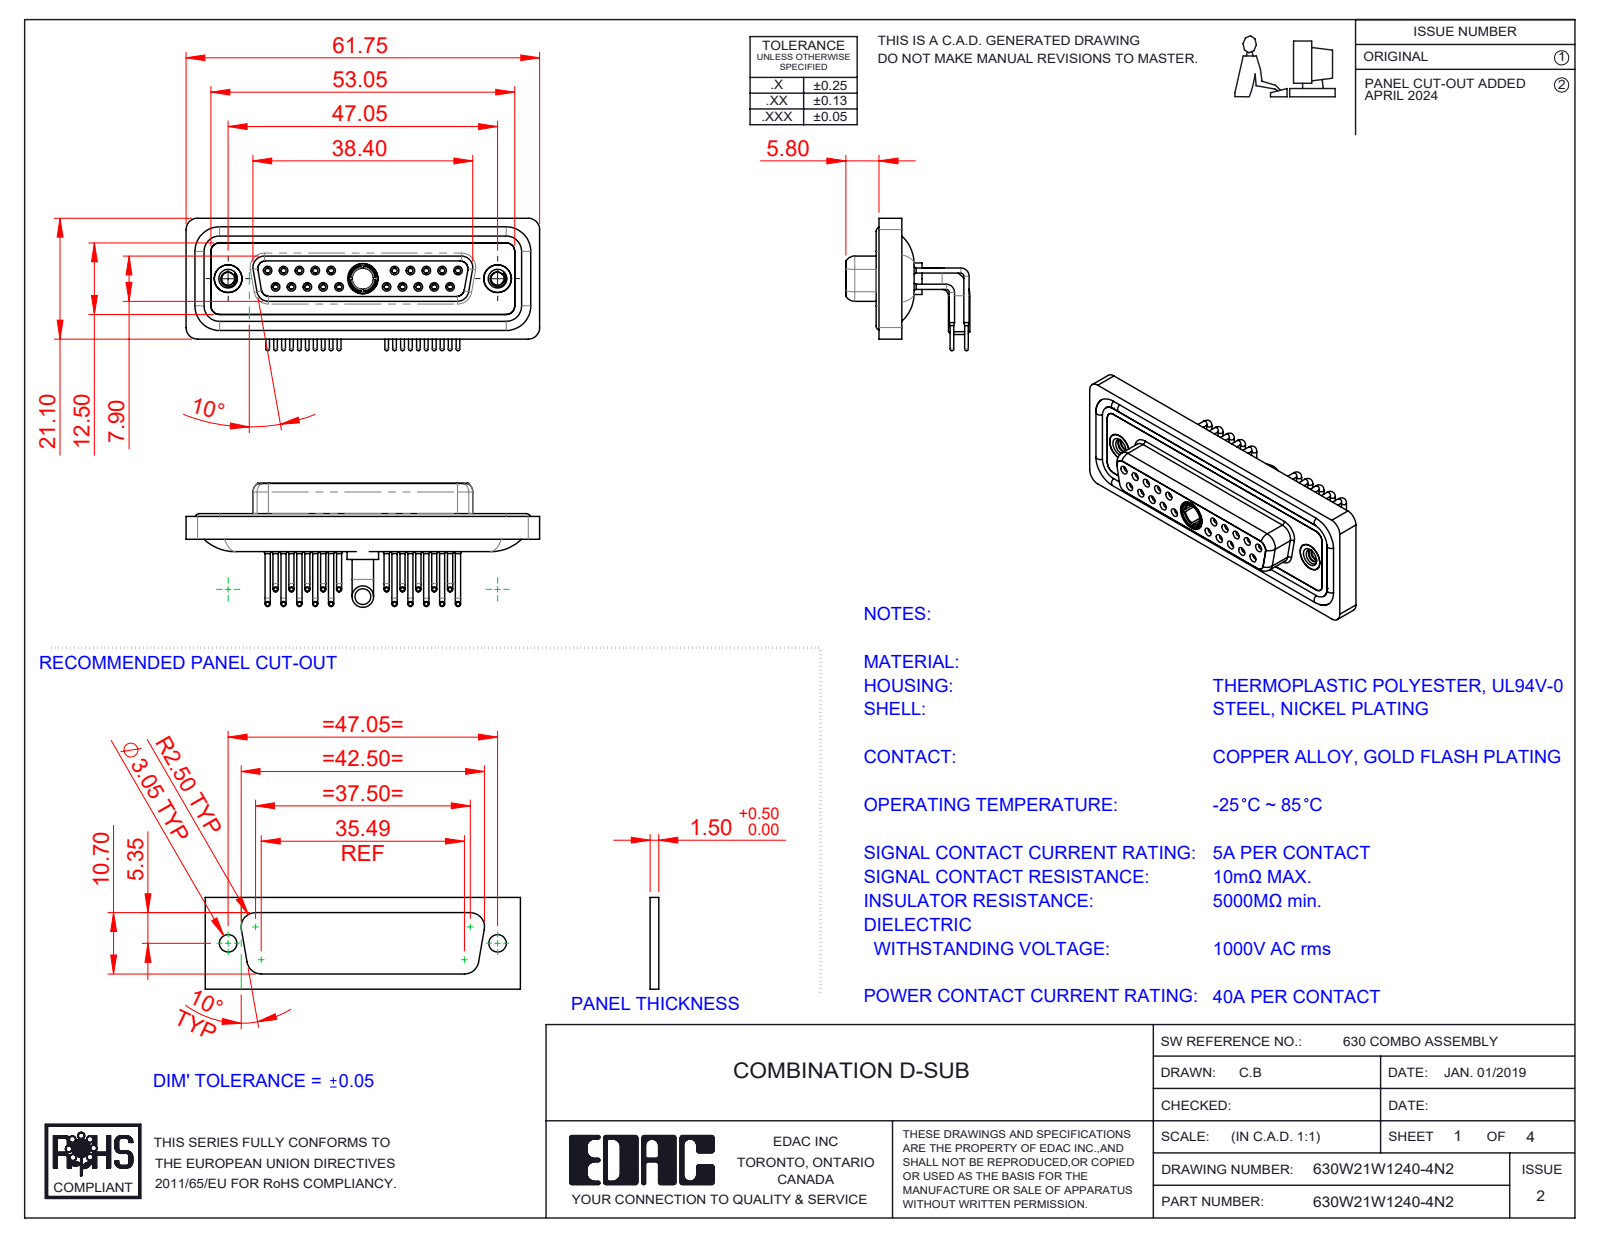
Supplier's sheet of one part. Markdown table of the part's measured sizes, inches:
| quantity | value |
| --- | --- |
| part name | Power Socket_40A RA; 630Combo Housing_21W1; 630Combo Threaded Rivet_2; 630W21W1140-4N2 (+5 more) |
| STEP written by | SolidWorks 2023 (CONFIG_CONTROL_DESIGN) |
| units | inches |
| bodies | 29 solids, 1524 faces (434 planar, 673 cylindrical, 417 other) |
| overall size | 2.431 × 0.91 × 0.854 |
| volume | 0.523 in³ |
| surface area | 22.98 in² |
| round holes (diameter × count) | 0.035 × 20, 0.043 × 20, 0.059 × 20, 0.079 × 20, 0.063 × 10, 0.067 × 10, 0.191 × 3, 0.089 × 2, 0.157 × 2, 0.159 × 2, 0.197 × 2, 0.146 × 1 |
| round bosses / shafts (diameter × count) | 0.035 × 20, 0.026 × 20, 0.063 × 14, 0.195 × 2, 0.189 × 2, 0.148 × 2, 0.217 × 1, 0.205 × 1 |
| partial cylindrical surfaces (radius × count) | 0.059 × 18, 0.079 × 18, 0.053 × 8, 0.063 × 8, 0.01 × 4, 0.02 × 4, 0.024 × 4, 0.026 × 4 |
| main face-to-face distances | 0.016, 0.071, 0.161, 0.063, 0.043, 0.098, 0.122, 0.059, 0.386, 0.018 |
| hole center spacings | 0.124, 0.109, 0.218, 0.327, 0.198, 0.763, 0.826, 0.872 |
